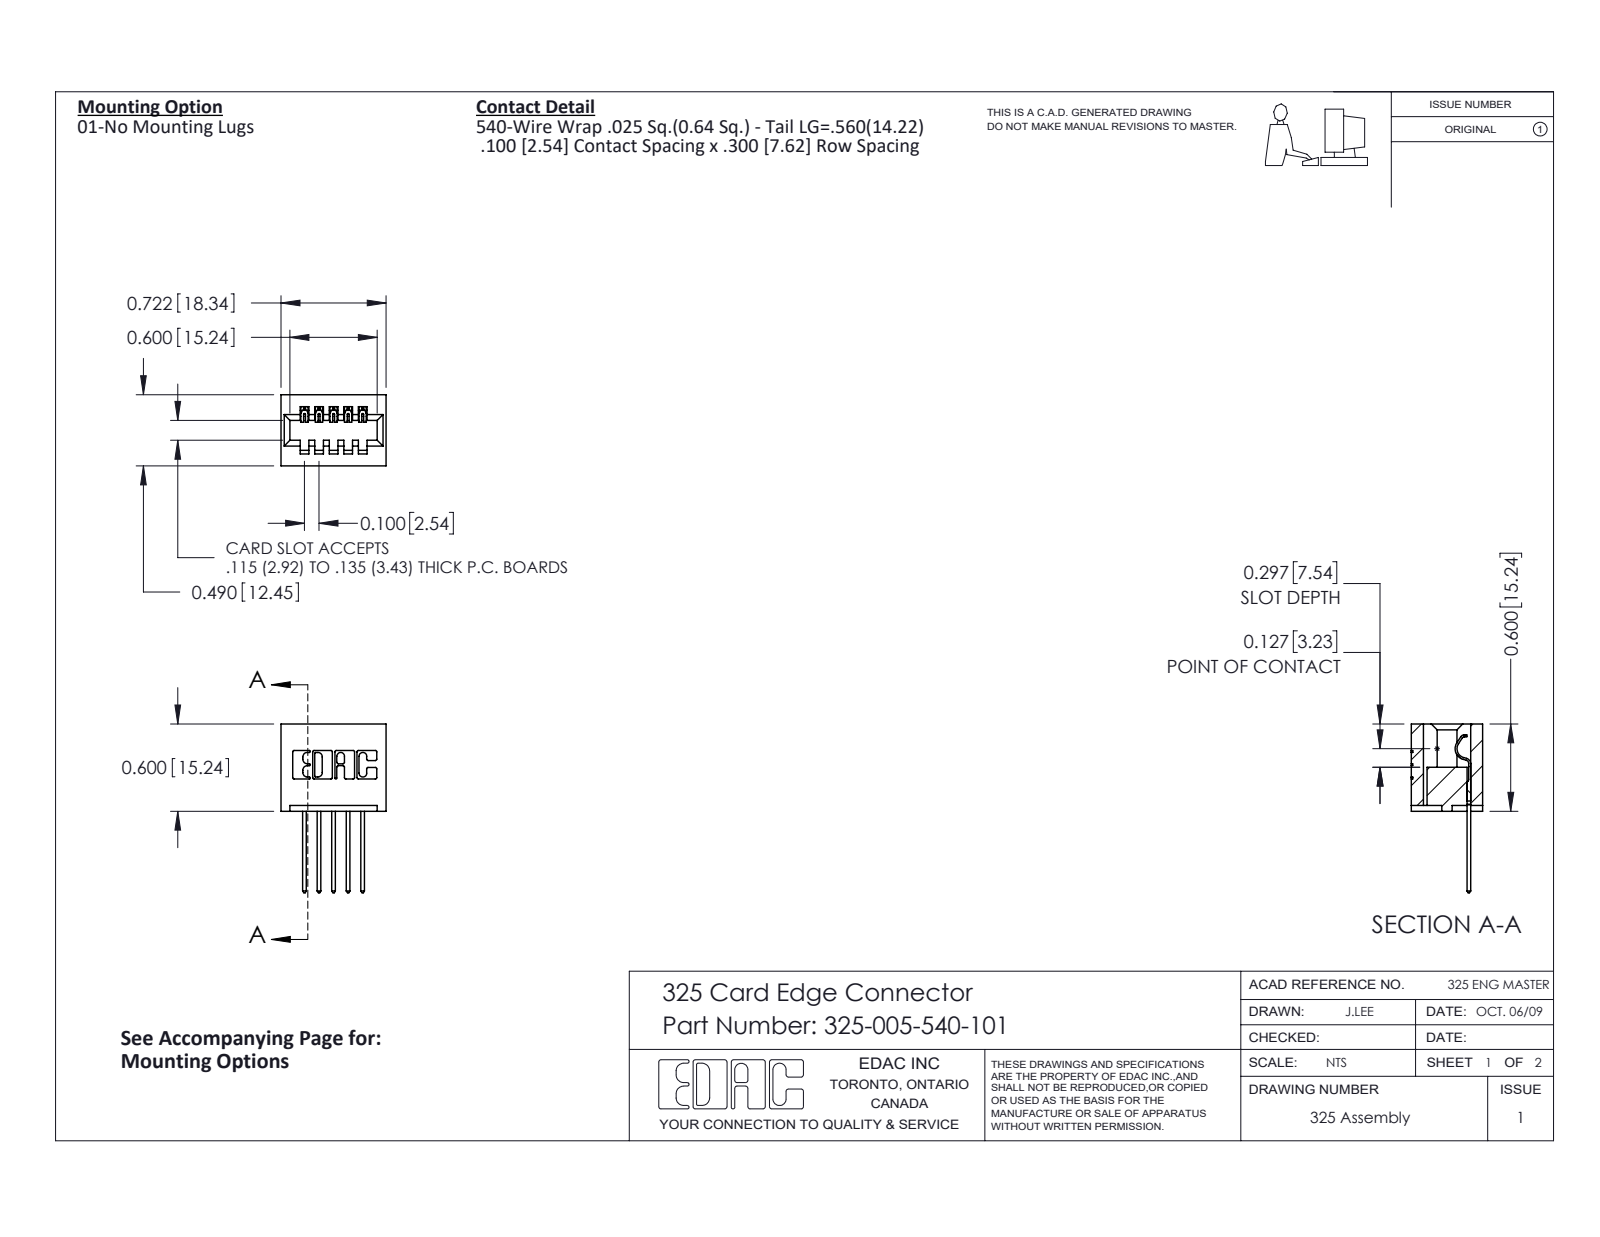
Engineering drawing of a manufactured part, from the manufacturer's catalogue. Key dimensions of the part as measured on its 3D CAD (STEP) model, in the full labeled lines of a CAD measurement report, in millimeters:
Part name (STEP PRODUCT): 325-292-001_325-293-140; 325 Part_Lugless; 325-005-540-101
STEP written by: SolidWorks 2016 (CONFIG_CONTROL_DESIGN)
Units: millimetres
Bodies: 6 solids, 396 faces (276 planar, 120 cylindrical, 0 other)
Overall size (bounding box): 29.5 × 18.3 × 12.4
Volume: 2 620 mm³ · Surface area: 2 770 mm²
Partial cylindrical surfaces — rounded edges, fillets, slot ends (radius × count): R0.3 ×22, R0.2 ×10, R0.3 ×10, R0.2 ×6, R0.8 ×6, R0.7 ×3, R0.4 ×1, R0.6 ×1
Main face-to-face distances: 2.5, 2.1, 7.6, 10.3, 5.1, 1, 12.4, 1.5, 9.7, 18.3
